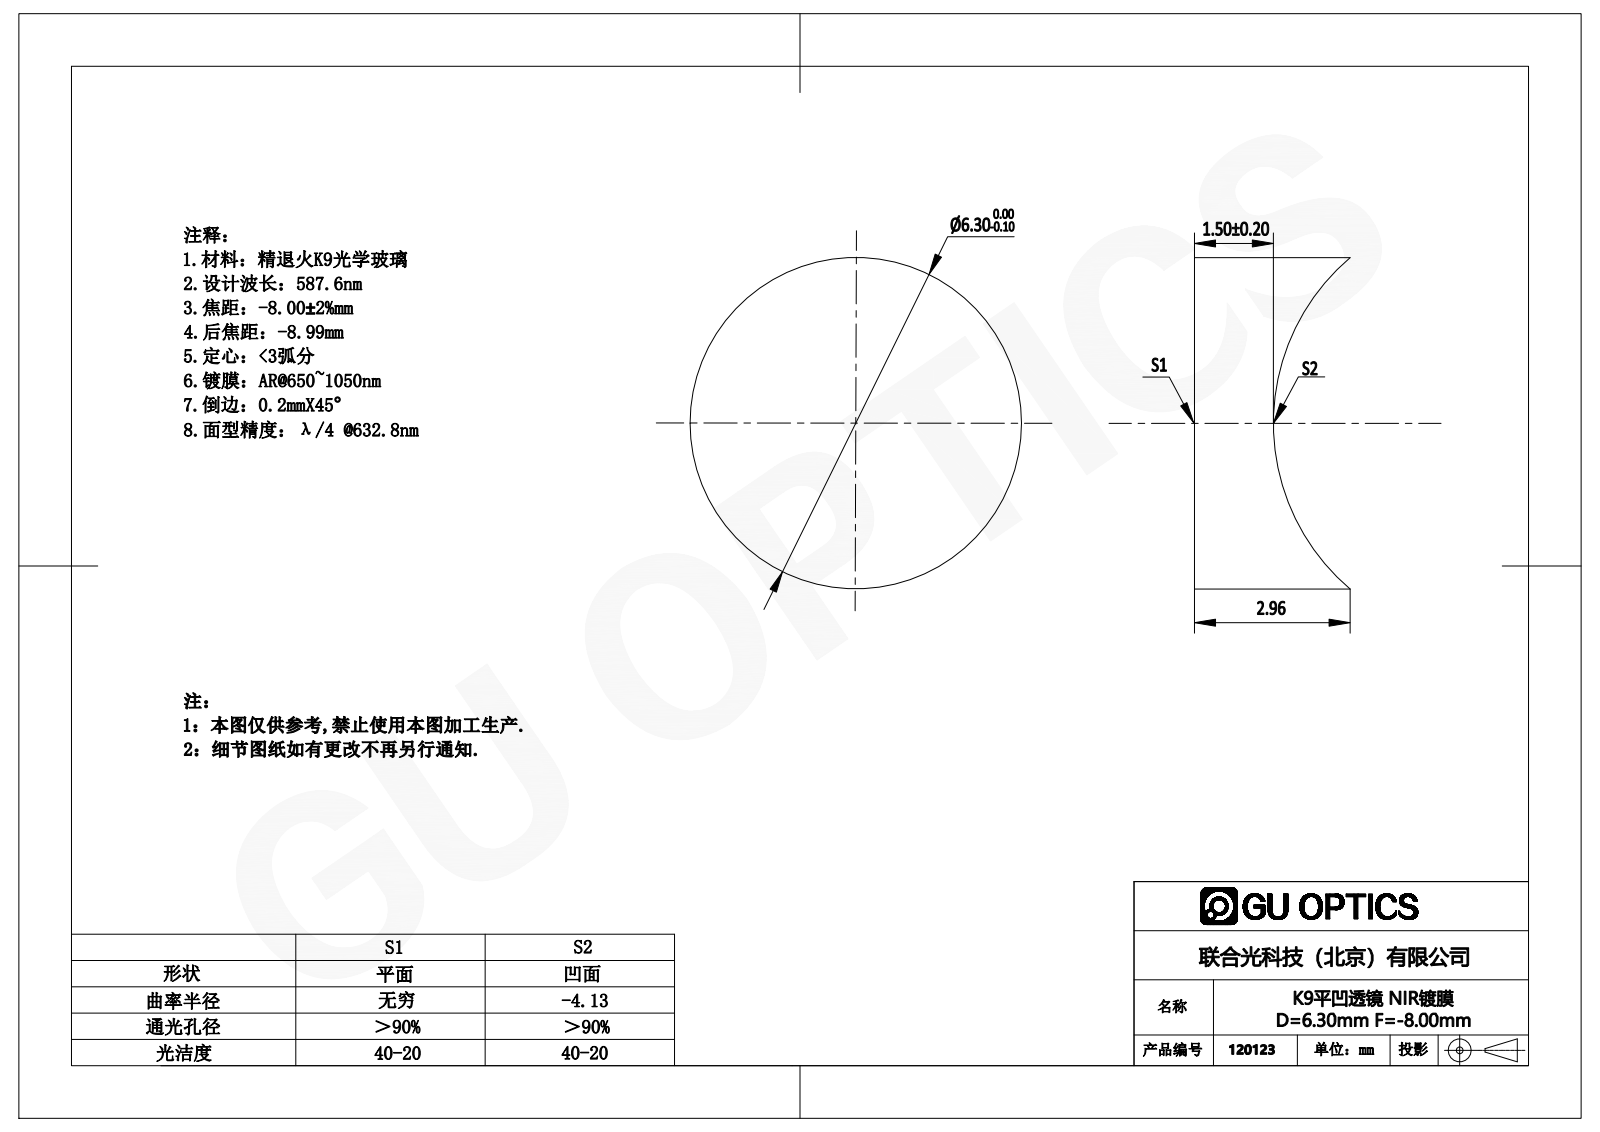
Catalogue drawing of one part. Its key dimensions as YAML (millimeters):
part_name: "120123"
step_written_by: "SolidWorks 2016 (AUTOMOTIVE_DESIGN)"
units: millimeters
bodies: {solids: 1, faces: 5, planar: 1, cylindrical: 2, other: 2}
overall_size: [6.3, 6.3, 2.96]
volume: 68
surface_area: 128
round_bosses_or_shafts:
  - {diameter: 6.3, count: 1}
